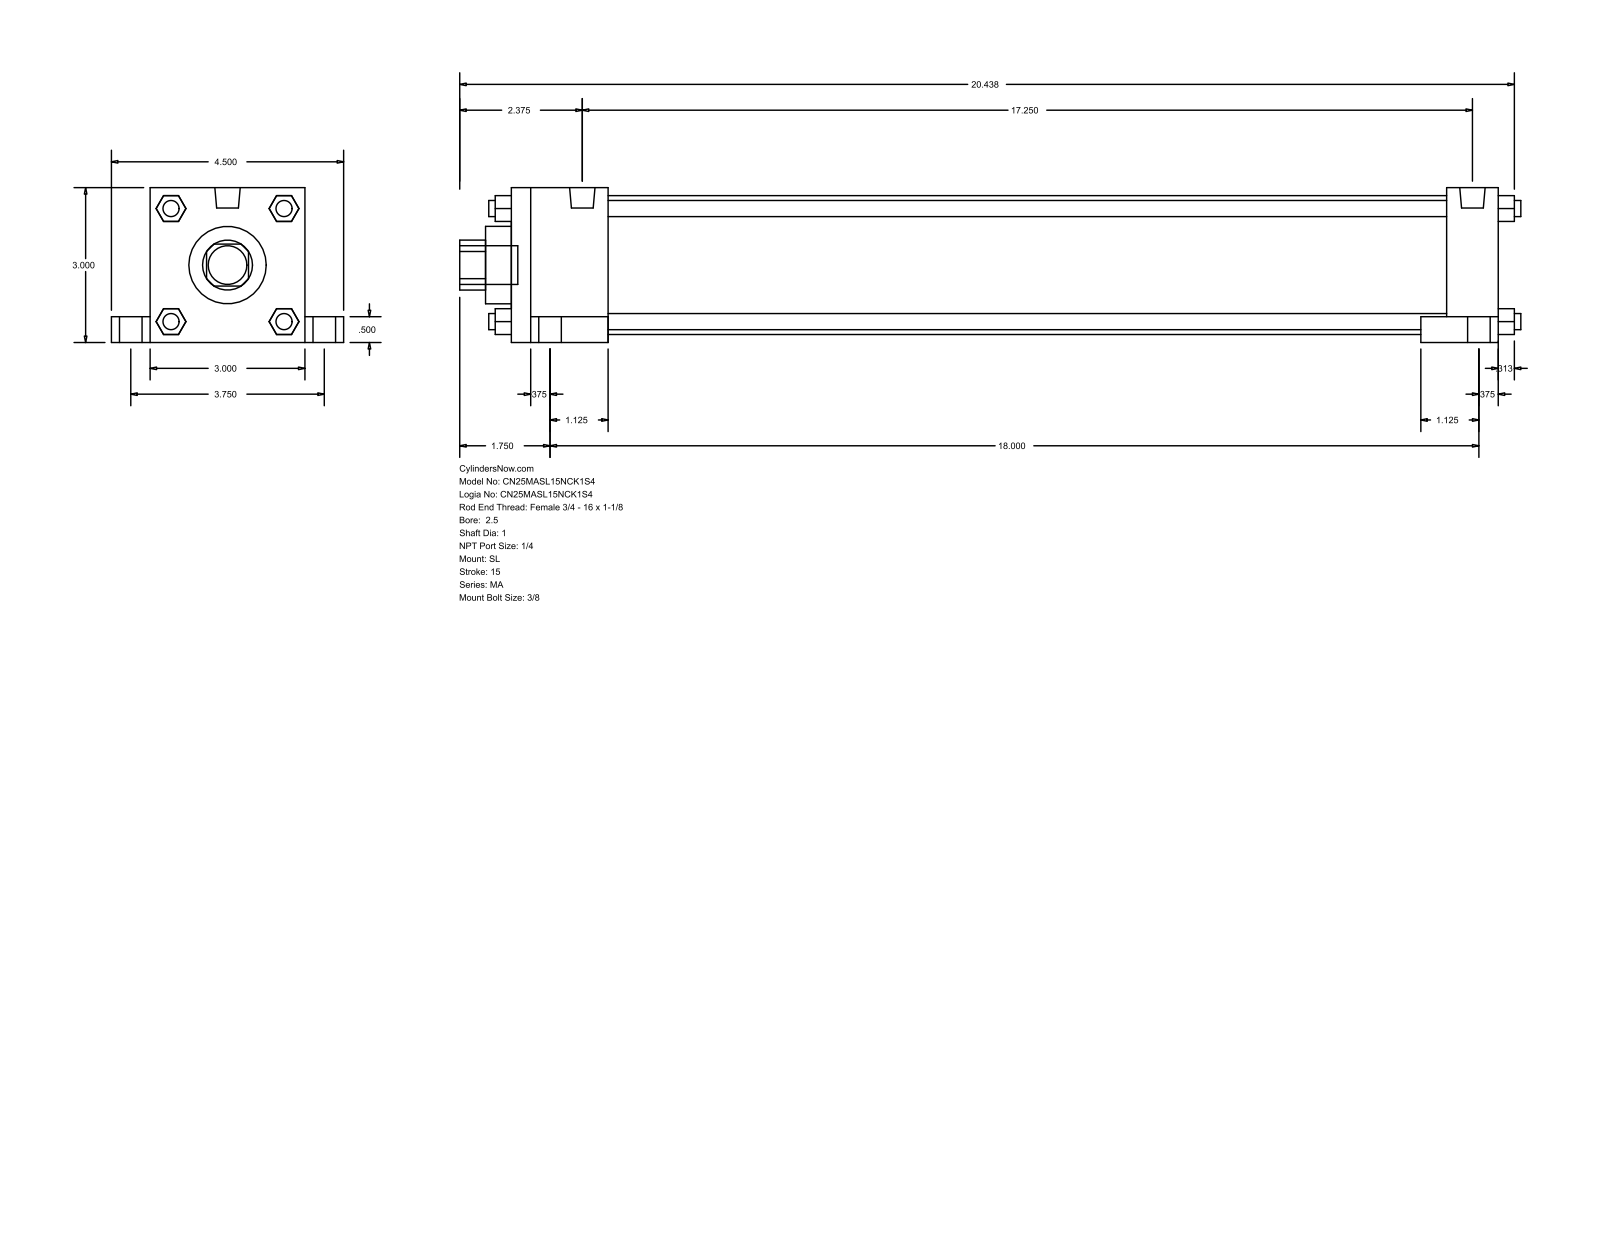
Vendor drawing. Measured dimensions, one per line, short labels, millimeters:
name: MA_SL__0250_1
written by: GSSL Pune (CONFIG_CONTROL_DESIGN)
unit: mm
bodies: 0 solids, 148 faces (112 planar, 36 cylindrical, 0 other)
size: 522.29 × 114.3 × 76.2
holes: 1× ⌀25.4, 1× ⌀38.1, 1× ⌀68.33
bosses: 8× ⌀7.94, 4× ⌀17.46, 4× ⌀11.11, 2× ⌀12.49, 1× ⌀19.05
rounds: 1× R12.29
face distances: 76.2, 485.78, 12.7, 47.63, 438.15, 460.37, 412.74, 25.41, 19.05, 95.25
